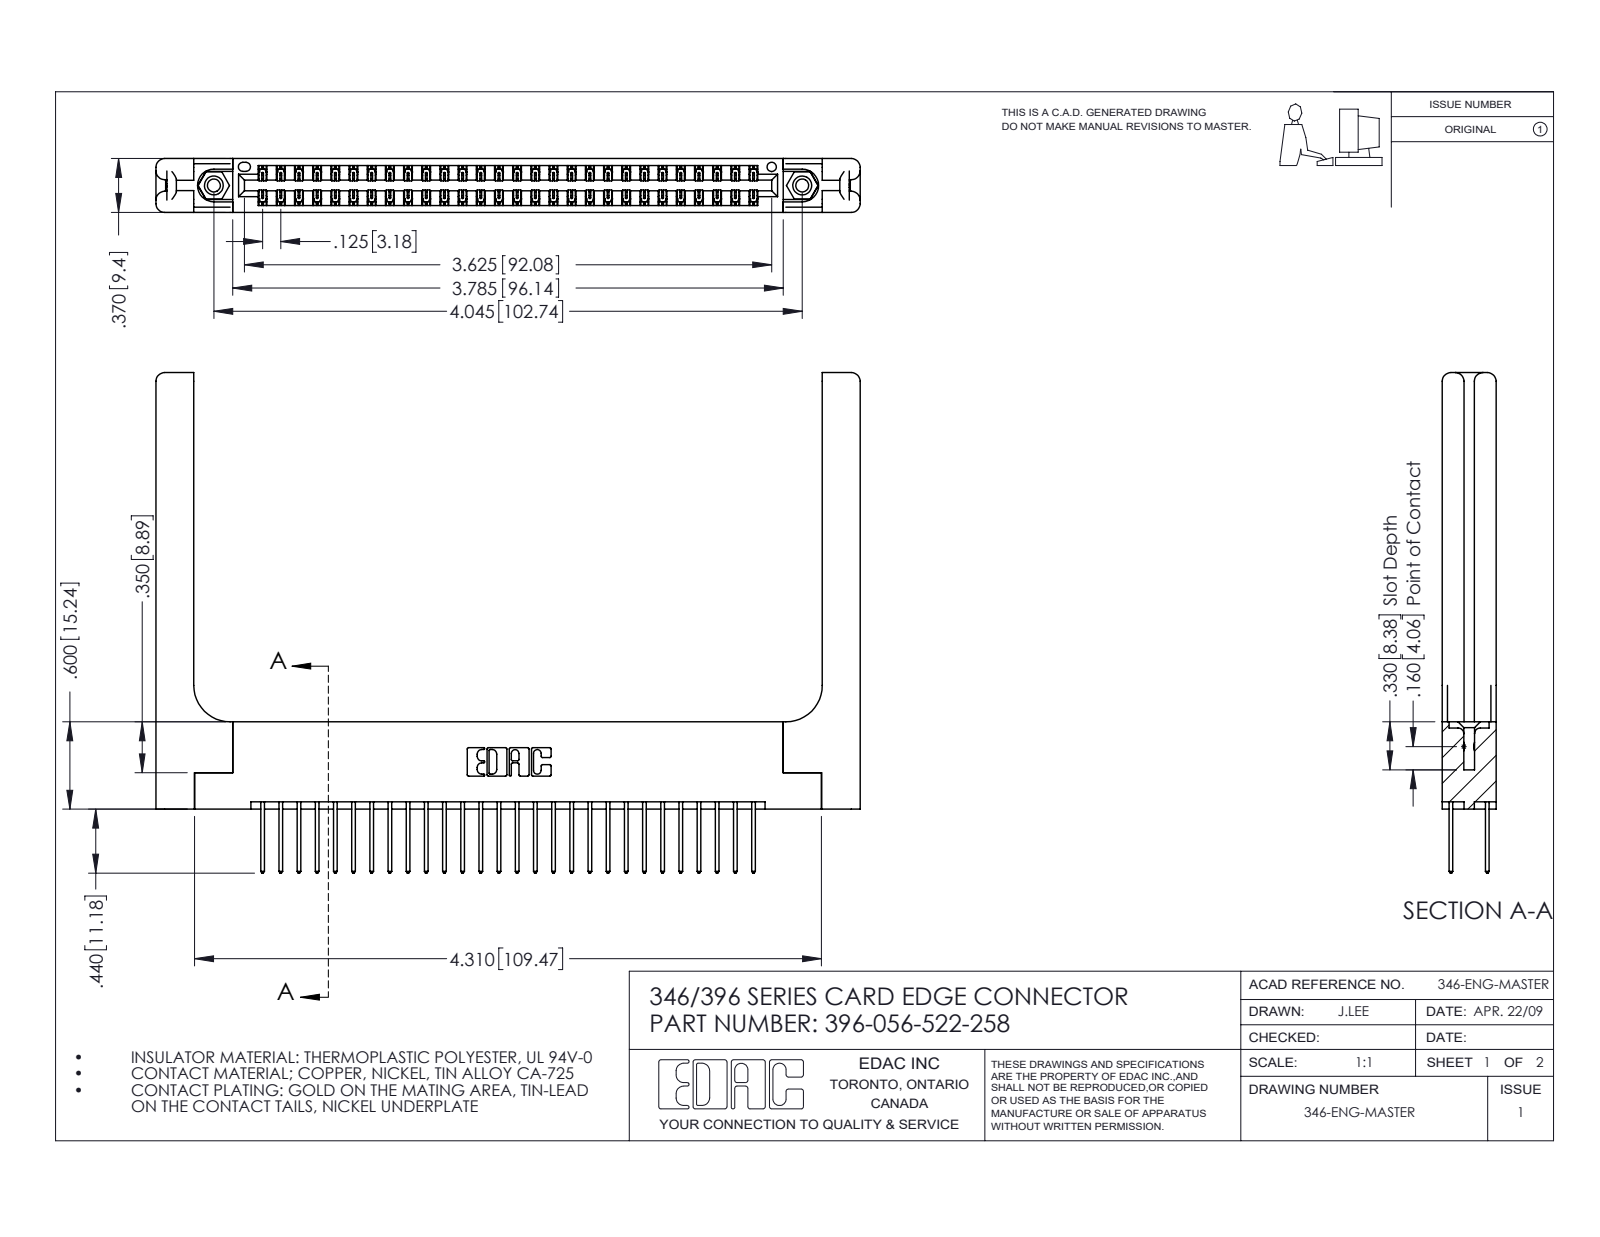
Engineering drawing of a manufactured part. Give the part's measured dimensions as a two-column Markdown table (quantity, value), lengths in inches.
| quantity | value |
| --- | --- |
| part name | 345-250-001_345-250-001-102; 345-292-001_345-293-122; 346-220-058_345-220-058; 346 Part_Flush Mounting Lugs - 0.156 Dia-TH (+1 more) |
| STEP written by | SolidWorks 2016 (CONFIG_CONTROL_DESIGN) |
| units | inches |
| bodies | 61 solids, 3290 faces (2184 planar, 1046 cylindrical, 60 other) |
| overall size | 4.841 × 3.44 × 0.37 |
| volume | 1.191 in³ |
| surface area | 34.02 in² |
| round holes (diameter × count) | 0.089 × 2, 0.125 × 2, 0.156 × 2, 0.064 × 1 |
| round bosses / shafts (diameter × count) | 0.155 × 2 |
| partial cylindrical surfaces (radius × count) | 0.006 × 84, 0.01 × 56, 0.01 × 22, 0.06 × 16, 0.007 × 6, 0.031 × 6, 0.026 × 3, 0.014 × 2 |
| main face-to-face distances | 0.37, 0.048, 0.322, 0.072, 0.25, 0.148, 0.15, 0.025, 0.298, 0.275 |
| hole center spacings | 0.246, 3.837, 4.045 |
